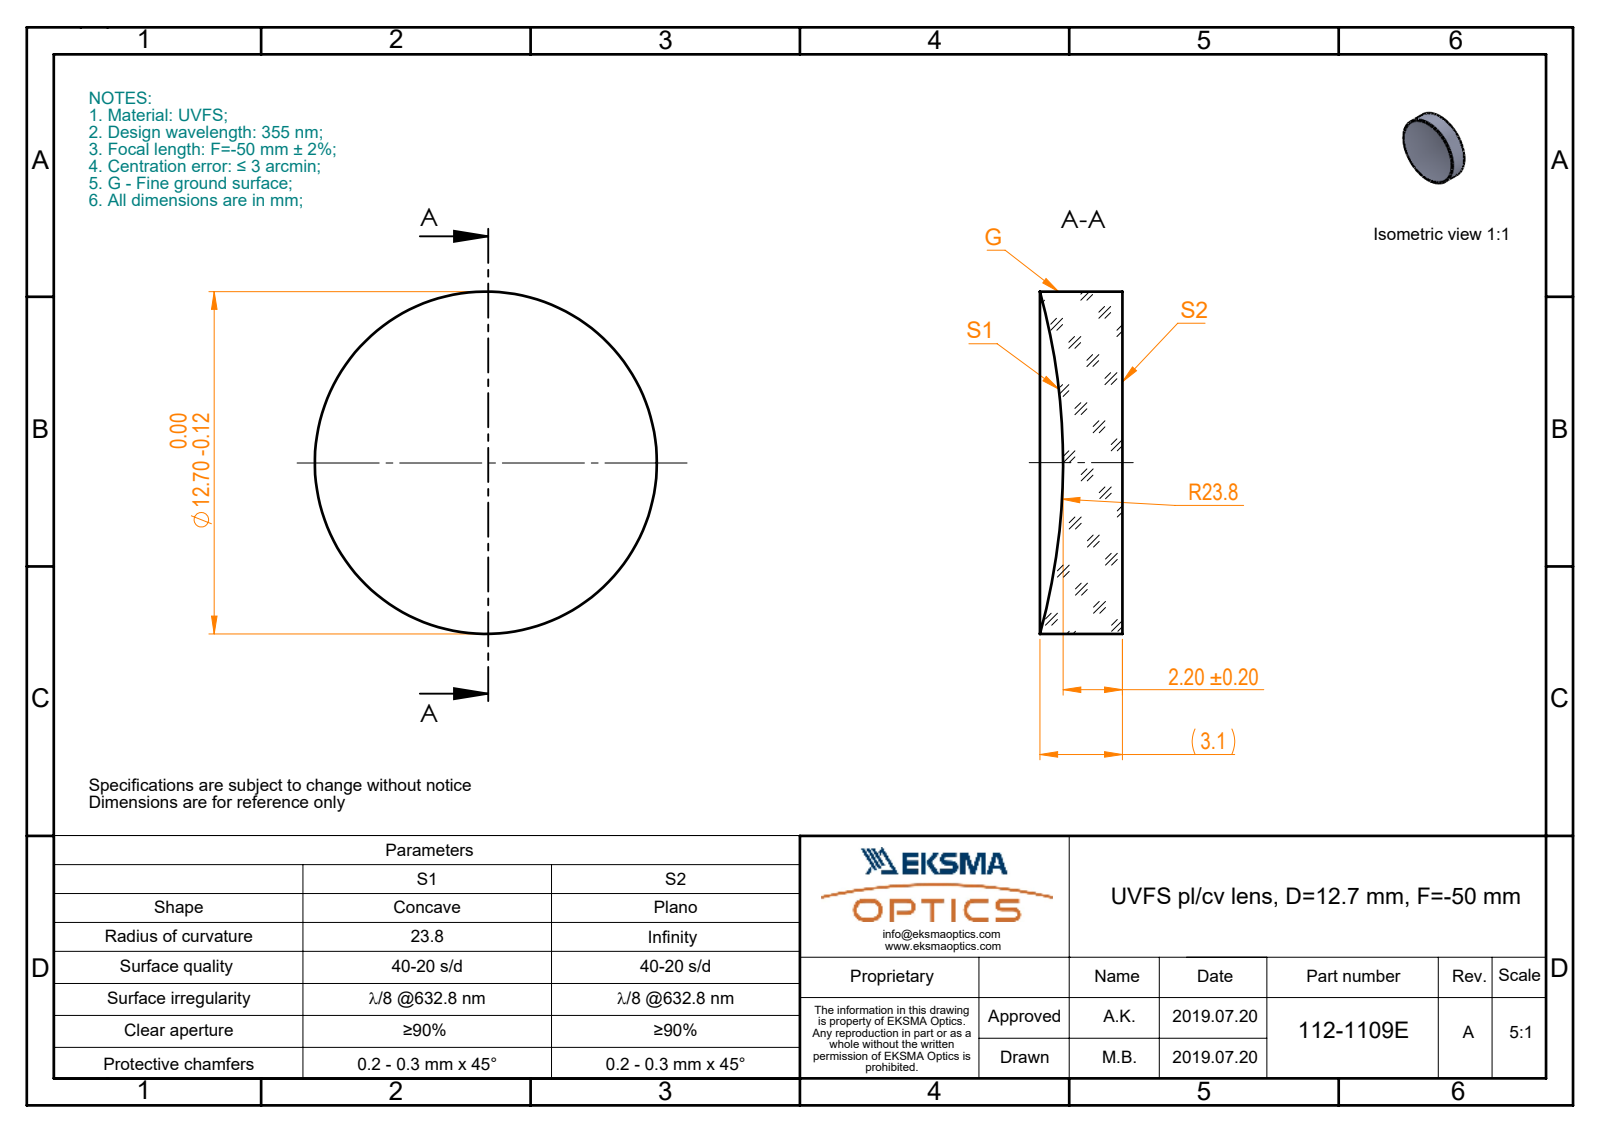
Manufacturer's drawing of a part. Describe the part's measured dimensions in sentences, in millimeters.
The part is named "112-1109E UVFS pl-cv 12.7 F-50". Its 3-D file was written by "SolidWorks 2017 (CONFIG_CONTROL_DESIGN)". It is 1 solid with 5 faces: 1 planar, 2 cylindrical and 2 other. Overall it measures 12.7 by 12.7 by 3.06 millimeters. Its volume is 333 cubic millimeters and its surface area 378 square millimeters. Round bosses or shafts: 1 of diameter 12.7.
